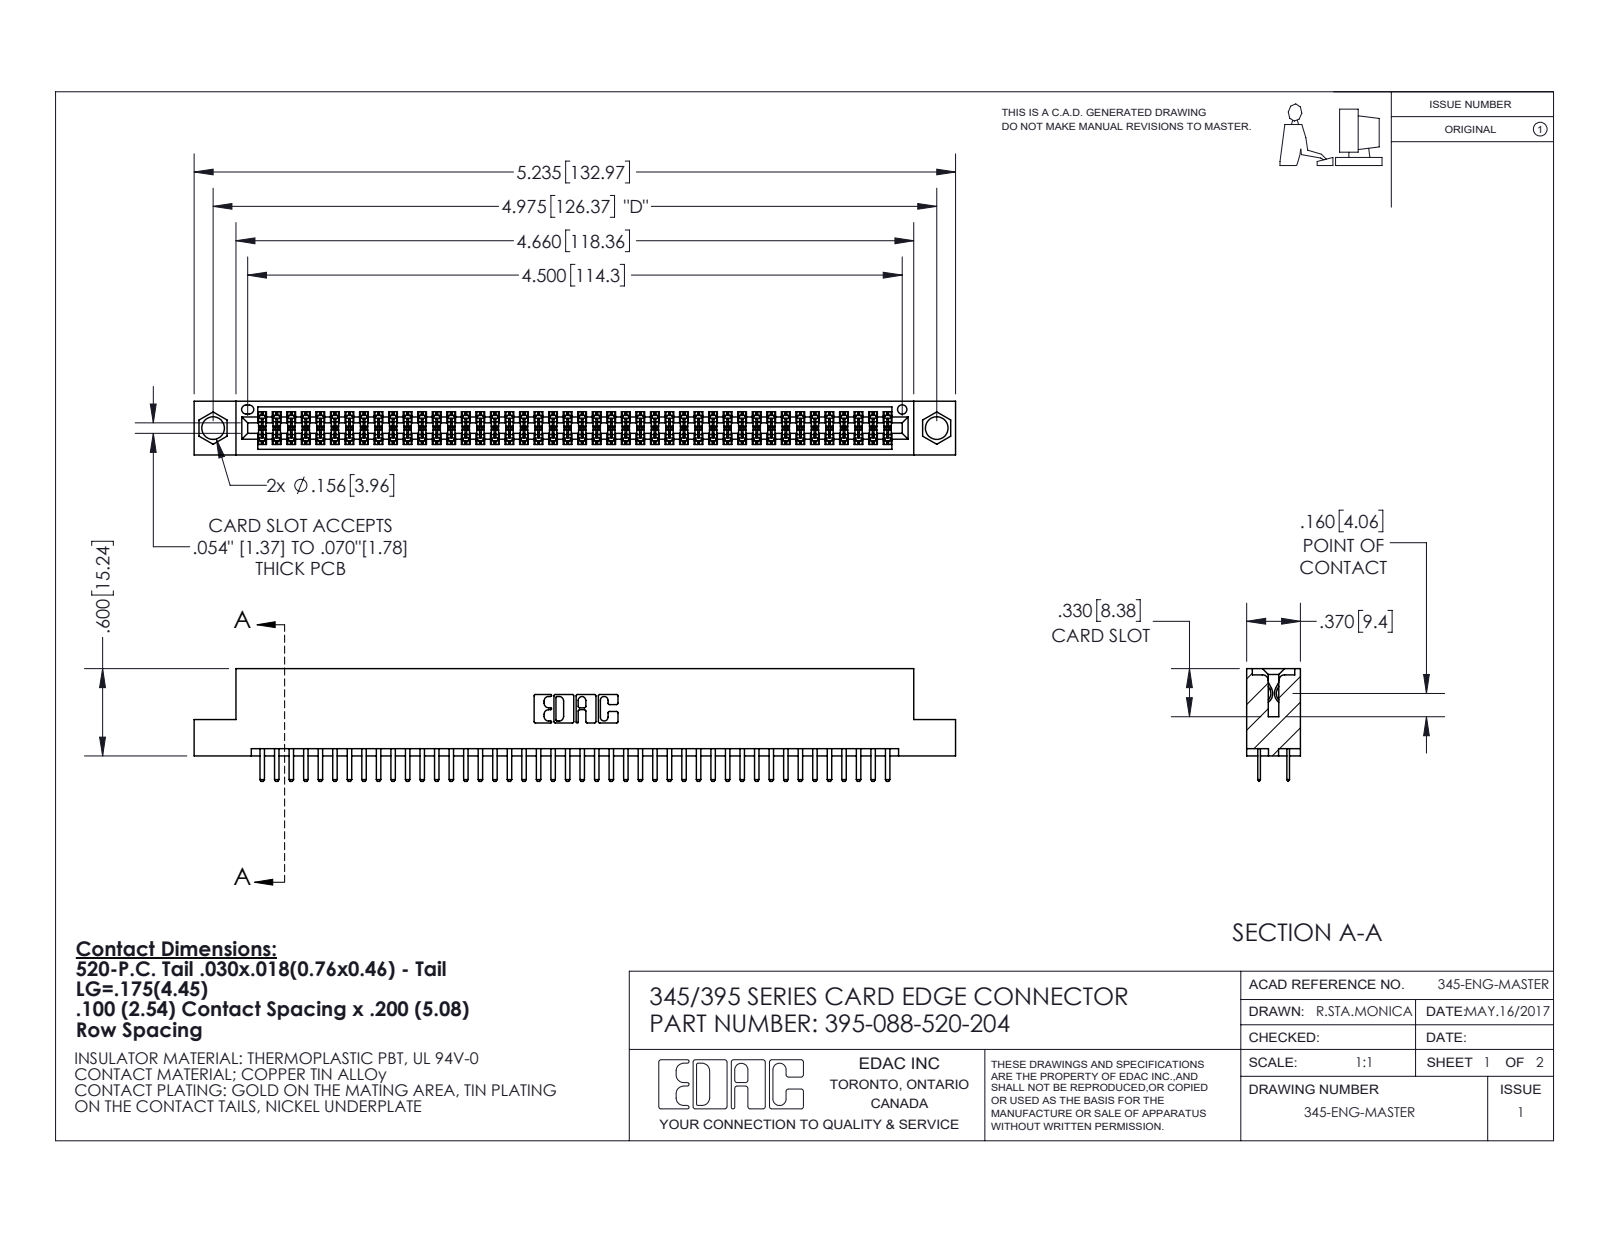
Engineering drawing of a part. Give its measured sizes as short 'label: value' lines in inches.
name: 345 Part_Flush Mounting Lugs - 0.156 Dia-TI; 345-292-001_345-293-120; 395-088-520-204
written by: SolidWorks 2020 (CONFIG_CONTROL_DESIGN)
unit: in
bodies: 89 solids, 4892 faces (3174 planar, 1718 cylindrical, 0 other)
size: 5.235 × 0.775 × 0.37
volume: 0.781 in³; area: 29.01 in²
holes: 2× ⌀0.156, 1× ⌀0.064
rounds: 176× R0.006, 92× R0.01, 22× R0.01, 6× R0.007, 6× R0.031, 3× R0.026, 2× R0.014, 2× R0.019
face distances: 0.072, 0.298, 0.2, 0.37, 0.098, 0.272, 0.025, 0.225, 0.022, 0.072
hole spacings: 0.27, 4.739, 4.975
